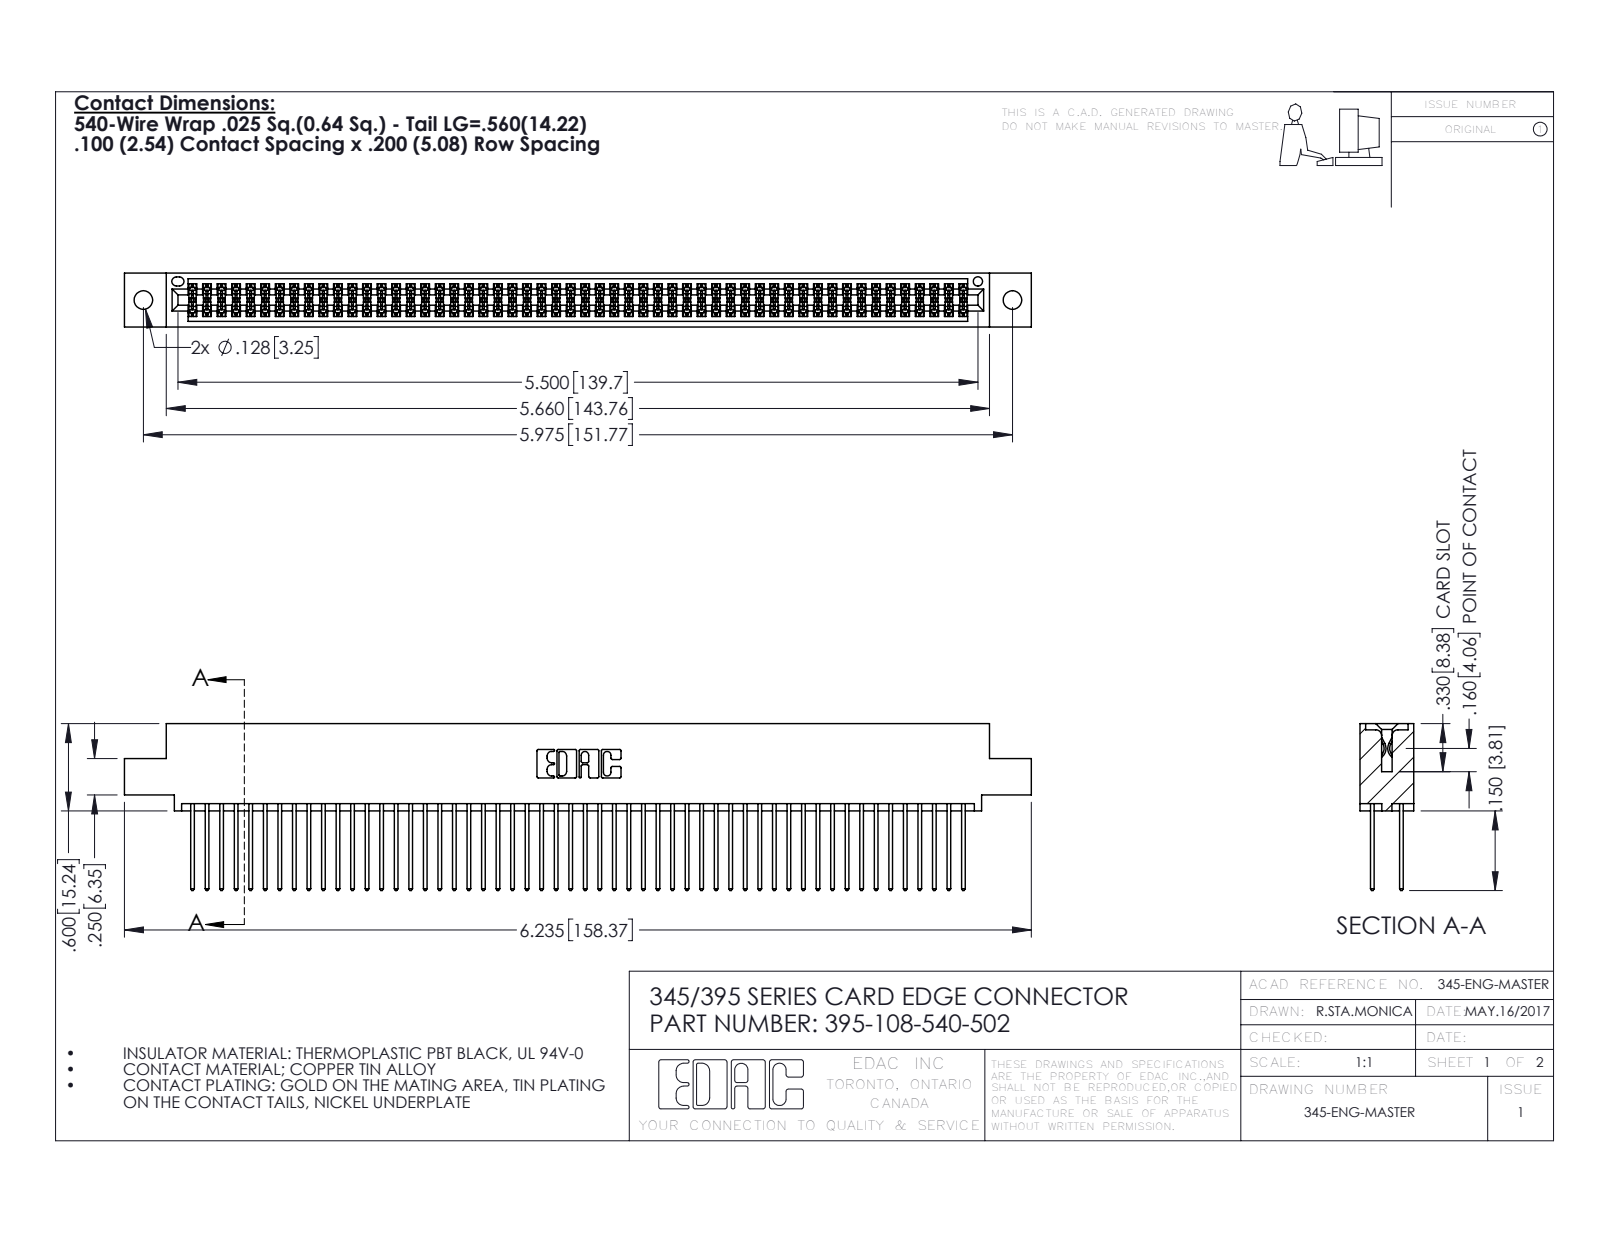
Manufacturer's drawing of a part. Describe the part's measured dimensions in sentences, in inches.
The part is named "395-108-540-502; 345-292-001_345-293-140; 345 Part_0.110 Offset - 0.128 Dia". Its 3-D file was written by "SolidWorks 2016 (CONFIG_CONTROL_DESIGN)". It is 109 solids with 5530 faces: 3648 planar, 1882 cylindrical and 0 other. Overall it measures 6.235 by 1.147 by 0.37 inches. Its volume is 0.964 cubic inches and its surface area 39.21 square inches. Round holes: 2 of diameter 0.128, 1 of diameter 0.064. Partial cylindrical surfaces (rounded edges, fillets, slot ends): 162 of radius 0.006, 108 of radius 0.01, 22 of radius 0.01, 6 of radius 0.007, 6 of radius 0.031, 3 of radius 0.026, 2 of radius 0.014, 2 of radius 0.019. The main face-to-face distances are 0.298, 0.072, 0.2, 0.098, 0.272, 0.025, 0.37, 0.225, 0.175, 0.149. The hole center spacings are 0.27, 5.739, 5.975.
